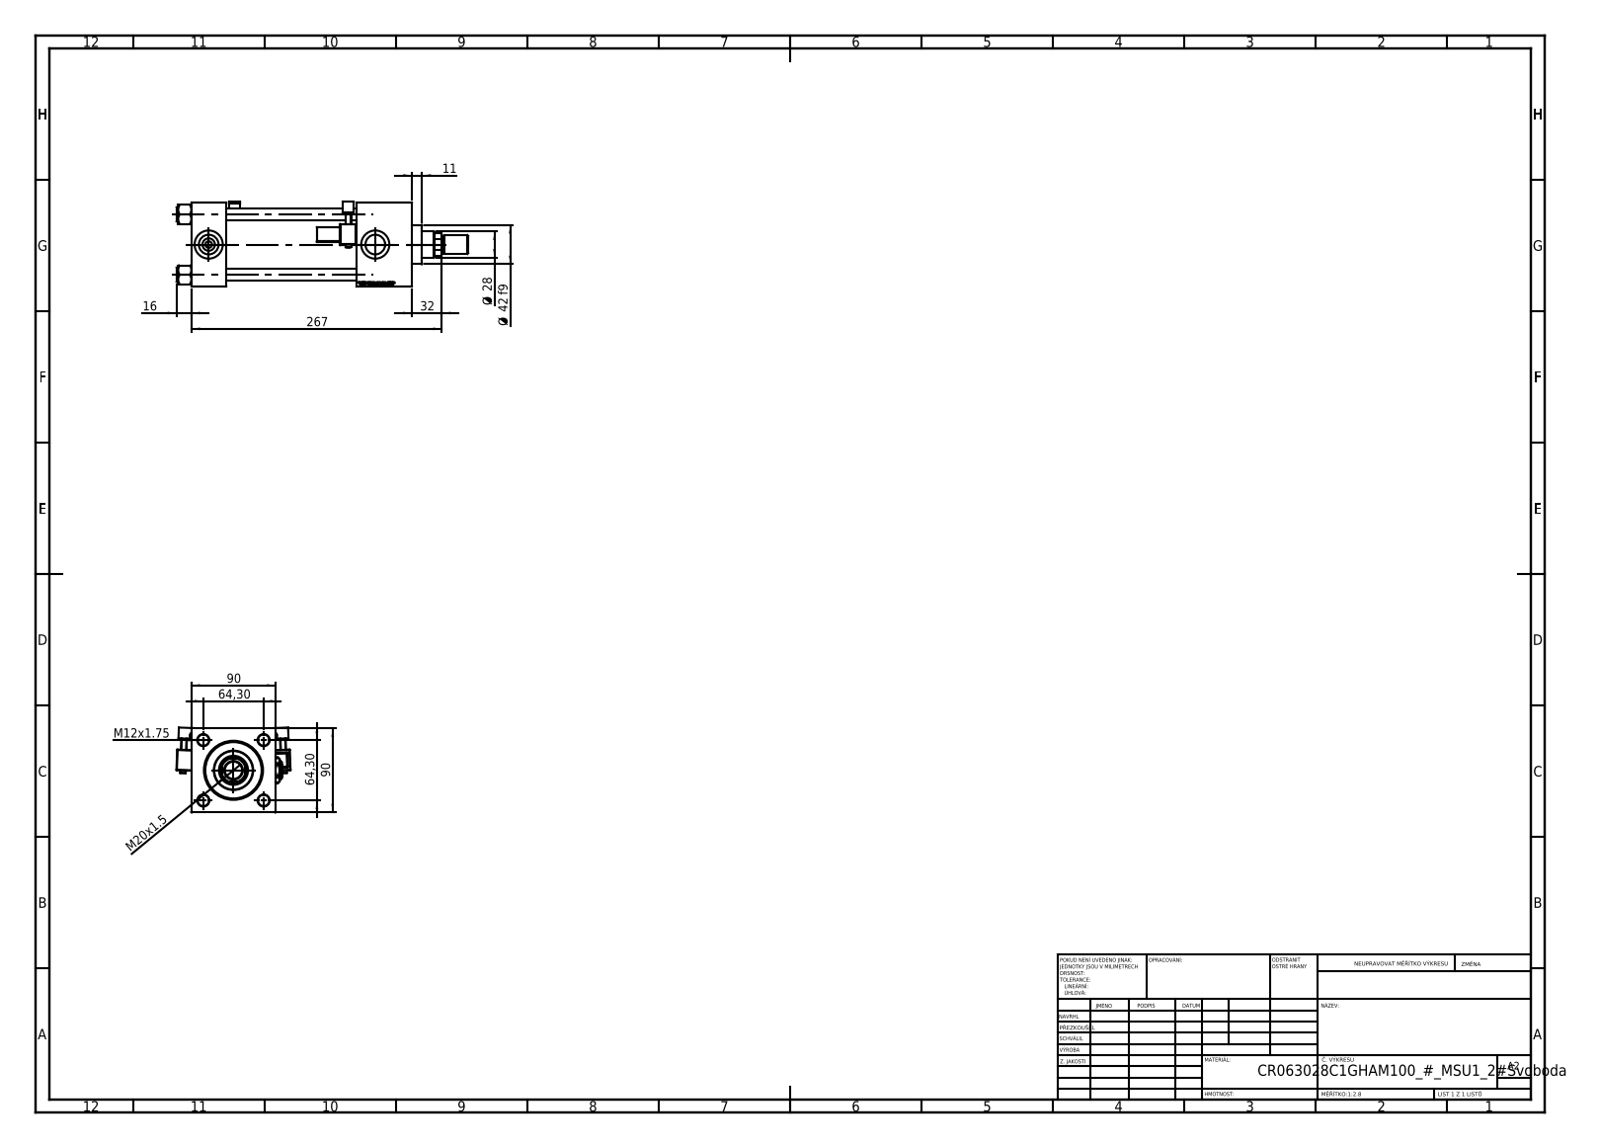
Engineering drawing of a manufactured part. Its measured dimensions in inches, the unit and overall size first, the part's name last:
Units: inches
Overall size (bounding box): 12.244 × 4.786 × 3.564
Round holes (diameter × count): ⌀0.472 ×4, ⌀0.276 ×2, ⌀0.825 ×2, ⌀1.181 ×2, ⌀0.728 ×1, ⌀1.102 ×1, ⌀1.22 ×1, ⌀1.969 ×1, ⌀2.362 ×1, ⌀2.48 ×1
Round bosses / shafts (diameter × count): ⌀0.591 ×4, ⌀0.236 ×2, ⌀2.717 ×1, ⌀1.654 ×1, ⌀0.787 ×1, ⌀0.709 ×1
Partial cylindrical surfaces — rounded edges, fillets, slot ends (radius × count): R0.02 ×48, R0.039 ×2, R0.098 ×2, R0.157 ×2, R0.531 ×1
Main face-to-face distances: 3.543, 1.457, 9.252, 7.795, 6.929, 5.472, 2.323, 8.122, 6.665, 1.193
Hole centre spacings: 1.79, 2.531, 3.58, 6.988
Volume: 68.77 in³ · Surface area: 384.8 in²
Bodies: 15 solids, 1364 faces (612 planar, 154 cylindrical, 598 other)
Part name (STEP PRODUCT): Zatka_pro_OIL_PORT; V215CR_C_TYCINKA; V215CR_C_Body; NUT_M5_C (+4 more)
STEP written by: SolidWorks 2019 (CONFIG_CONTROL_DESIGN)
